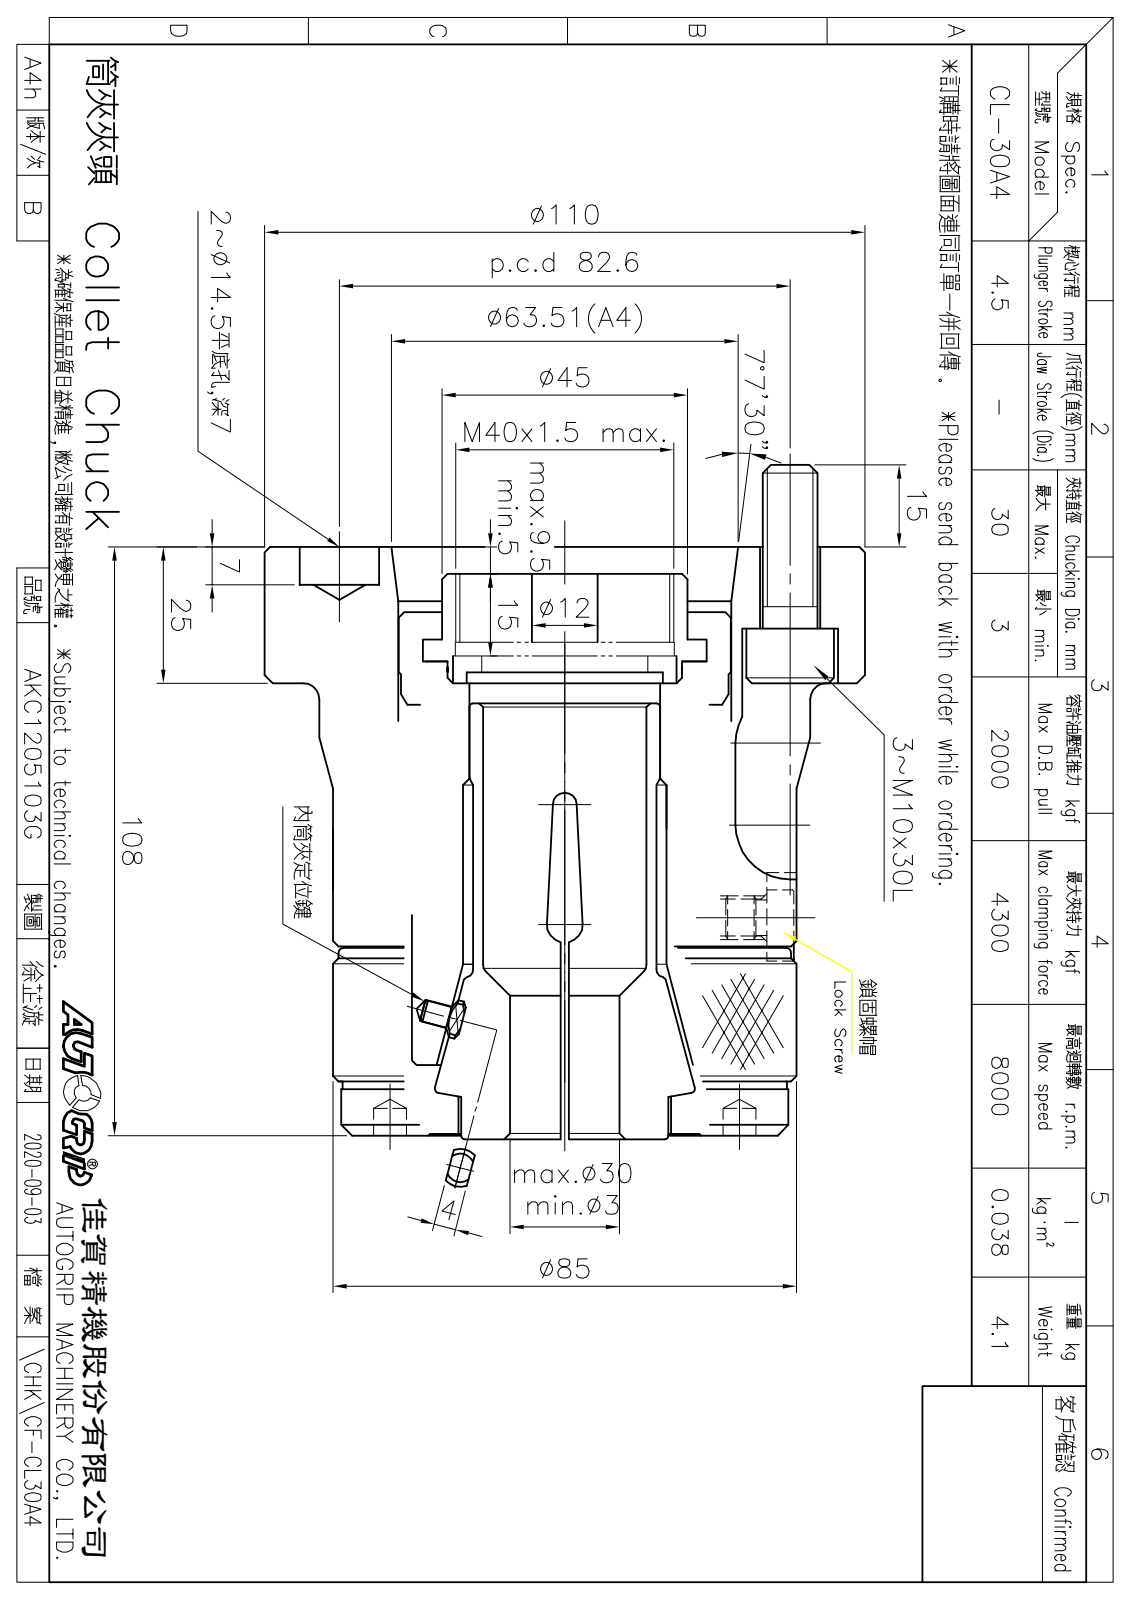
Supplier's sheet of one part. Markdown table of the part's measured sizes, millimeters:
| quantity | value |
| --- | --- |
| part name | CF-CL-30A4; CF-CL-30-02000; FSW320300; CF-CL-42-11000 (+4 more) |
| STEP written by | SolidWorks 2020 (CONFIG_CONTROL_DESIGN) |
| units | millimeters |
| bodies | 9 solids, 216 faces (96 planar, 60 cylindrical, 60 other) |
| overall size | 118 × 110 × 110 |
| volume | 536 770 mm³ |
| surface area | 131 122 mm² |
| round holes (diameter × count) | 11 × 3, 17.5 × 3, 5 × 2, 14.5 × 2, 4 × 1, 6.8 × 1, 30.5 × 1, 35 × 1, 36 × 1, 37.3 × 1, 38.5 × 1, 39 × 1 |
| round bosses / shafts (diameter × count) | 16 × 3, 10 × 3, 110 × 1, 90 × 1, 85 × 1, 83 × 1, 82 × 1, 81.4 × 1 |
| partial cylindrical surfaces (radius × count) | 8.5 × 3, 10 × 3, 3.5 × 1, 8 × 1, 8.25 × 1 |
| main face-to-face distances | 83, 108, 13, 25, 9, 4, 8, 5, 73.3, 48.3 |
| hole center spacings | 41.3, 71.54, 21.09, 21.38, 31.5, 37.38, 51.94, 58.41 |
